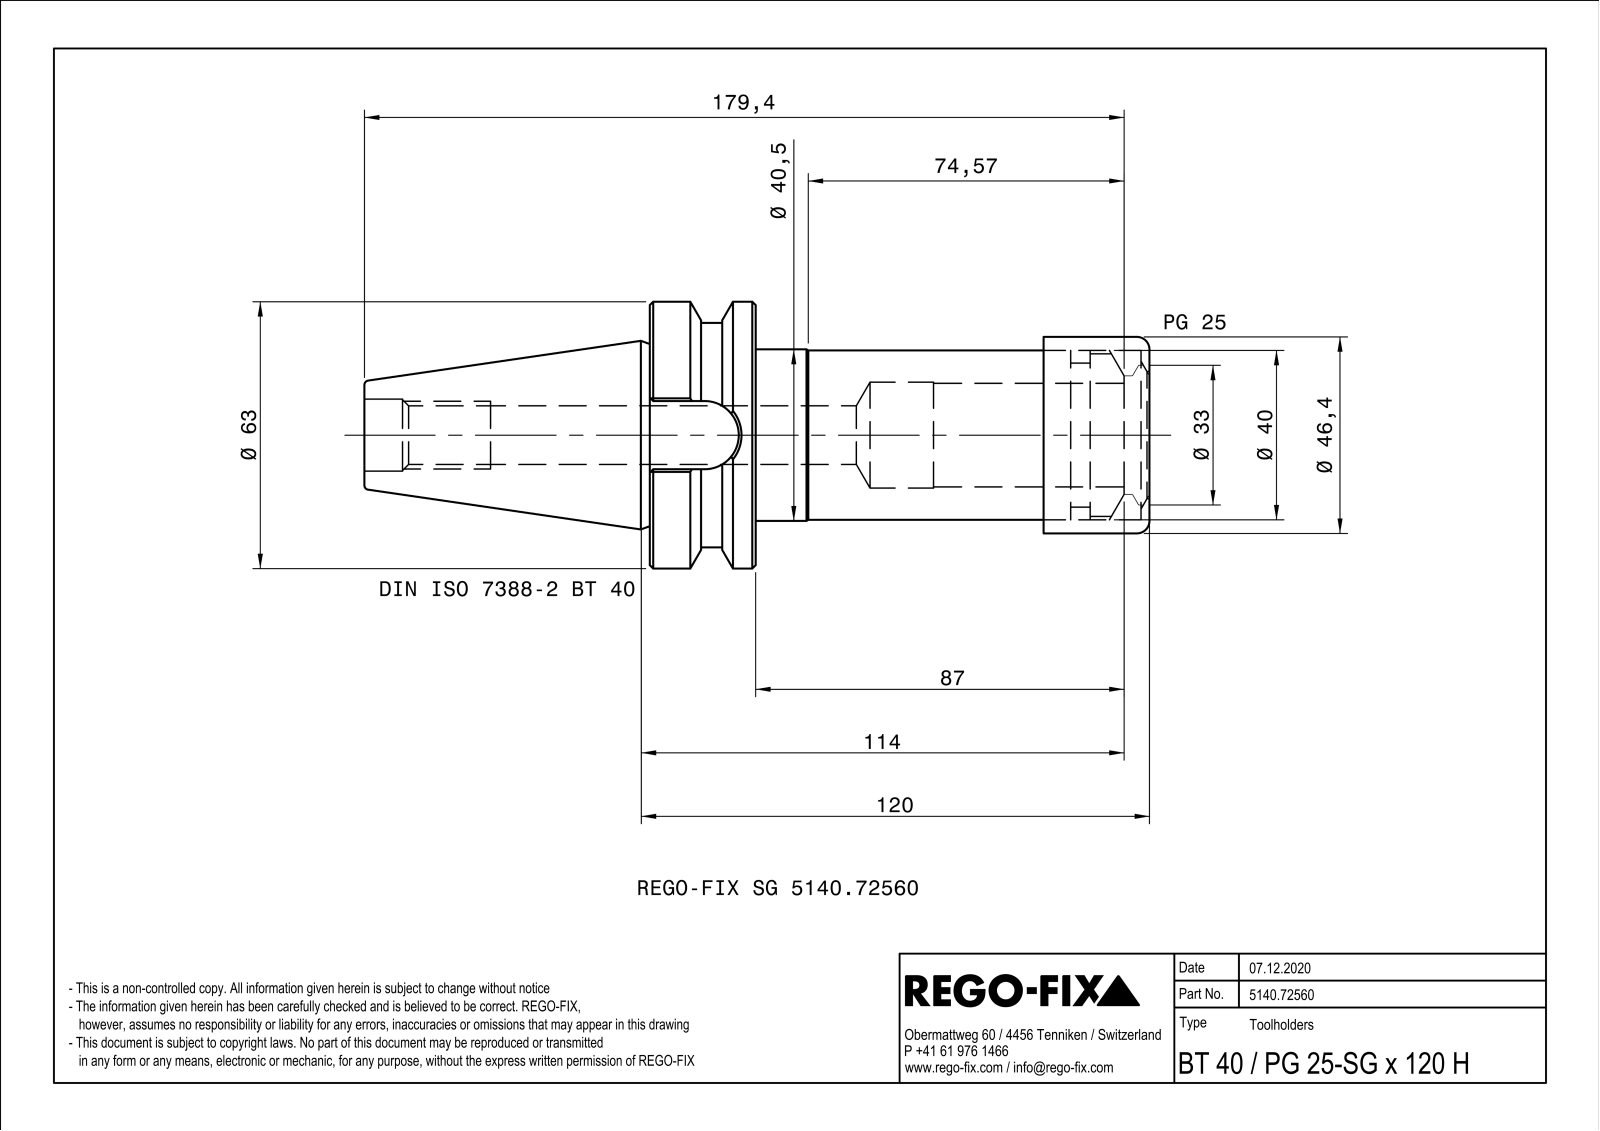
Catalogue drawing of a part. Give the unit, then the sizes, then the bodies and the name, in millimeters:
Units: millimetres
Overall size (bounding box): 185.4 × 63 × 63
Round holes (diameter × count): ⌀13.84 ×1, ⌀17.4 ×1, ⌀25 ×1, ⌀30 ×1, ⌀38.38 ×1, ⌀40.05 ×1, ⌀42 ×1
Round bosses / shafts (diameter × count): ⌀63 ×1, ⌀53 ×1, ⌀46.4 ×1, ⌀46 ×1, ⌀40.5 ×1, ⌀40 ×1, ⌀34 ×1
Partial cylindrical surfaces — rounded edges, fillets, slot ends (radius × count): R0.5 ×4, R8.05 ×1
Main face-to-face distances: 25, 93, 118, 68, 45.1, 18.6, 6.4, 74.4, 99.4, 14
Volume: 203 098 mm³ · Surface area: 46 439 mm²
Bodies: 1 solid, 101 faces (35 planar, 25 cylindrical, 41 other)
Part name (STEP PRODUCT): NOCUT
STEP written by: SIEMENS PLM Software Solid Edge ST10 (AUTOMOTIVE_DESIGN)
